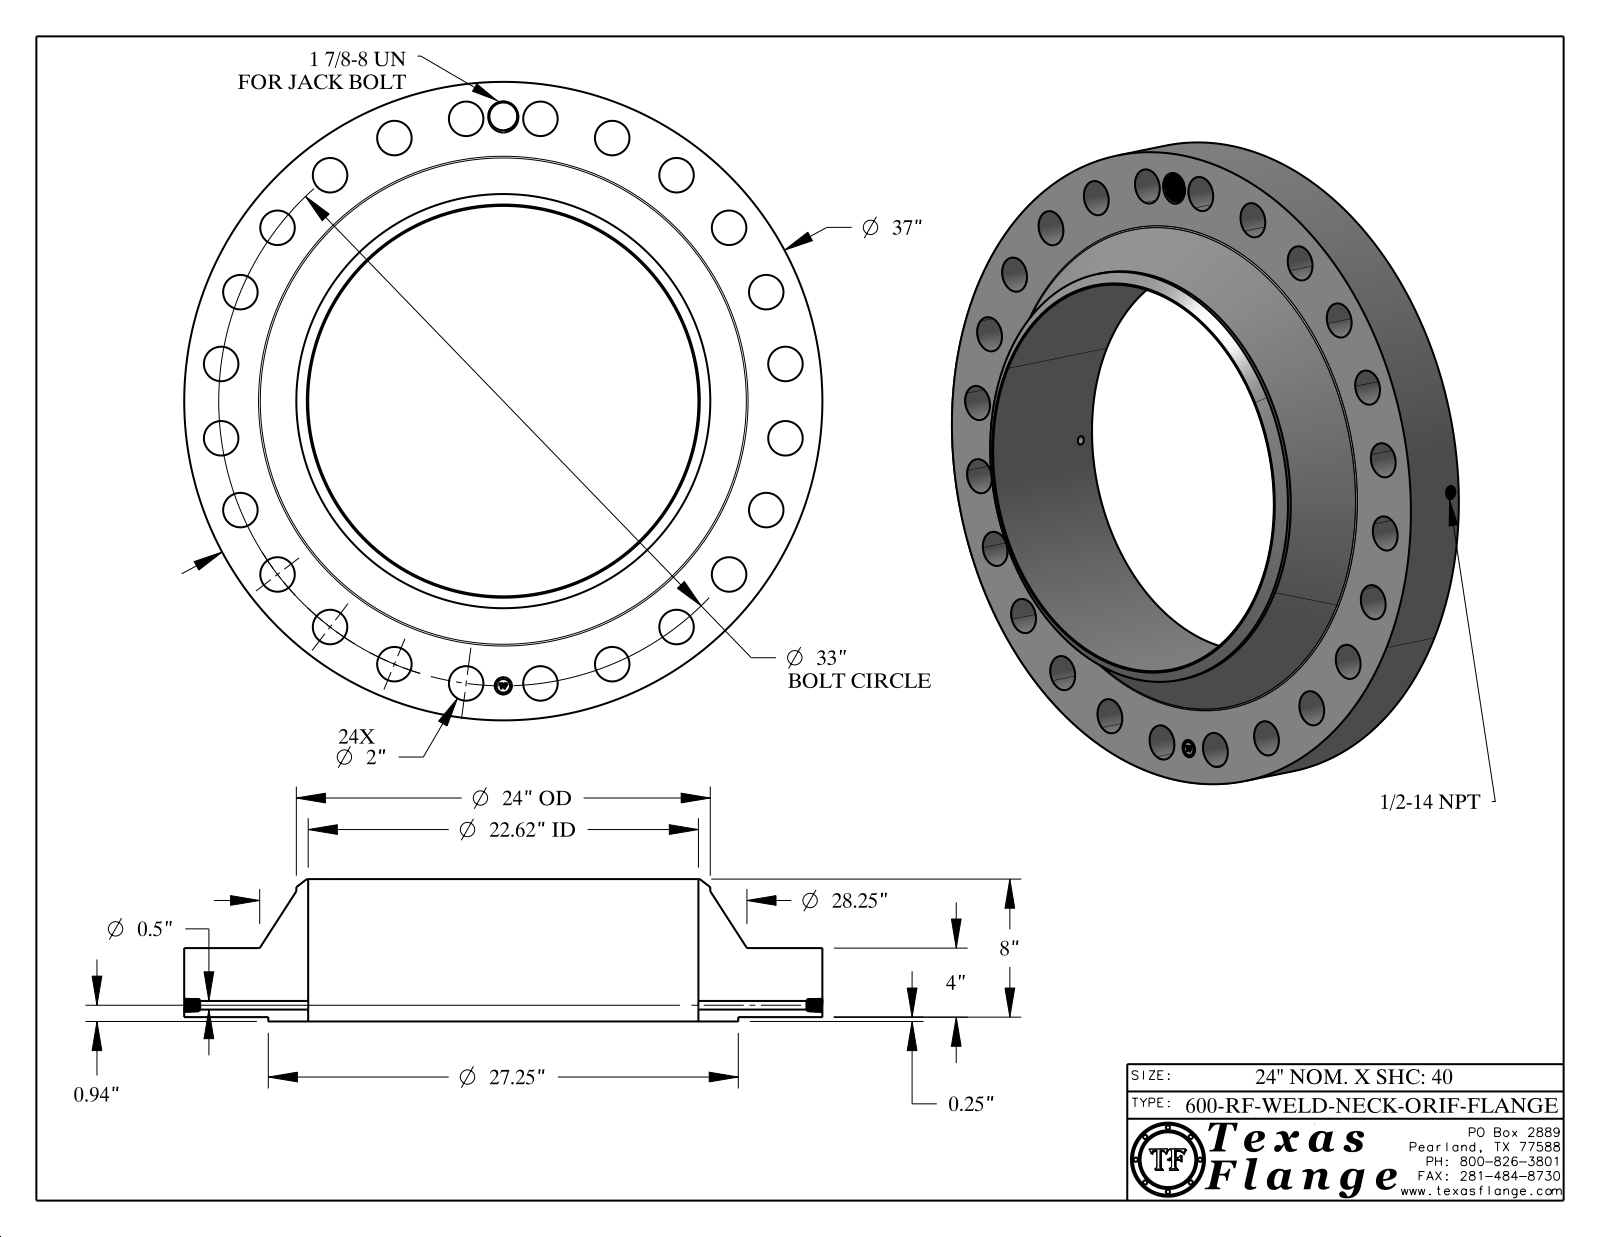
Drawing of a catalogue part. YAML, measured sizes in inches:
part_name: "600-RF-WELD-NECK"
step_written_by: "CATIA V5 STEP AP214 (AUTOMOTIVE_DESIGN)"
units: inches
bodies: {solids: 1, faces: 903, planar: 369, cylindrical: 159, other: 375}
overall_size: [37, 37, 8.25]
volume: 2894
surface_area: 3119
round_holes:
  - {diameter: 2, count: 24}
  - {diameter: 0.5, count: 1}
  - {diameter: 0.672, count: 1}
  - {diameter: 1, count: 1}
  - {diameter: 1.615, count: 1}
  - {diameter: 22.624, count: 1}
round_bosses_or_shafts:
  - {diameter: 0.061, count: 8}
  - {diameter: 37, count: 1}
  - {diameter: 27.25, count: 1}
  - {diameter: 24, count: 1}
  - {diameter: 0.788, count: 1}
face_to_face_distances: [4, 0.25, 4.25, 8.25, 8, 4.235, 3.985, 0.015, 4.015, 0.298]
hole_center_spacings: [16.5, 8.541, 20.089, 28.579, 12.628, 4.307, 23.334, 26.181]
